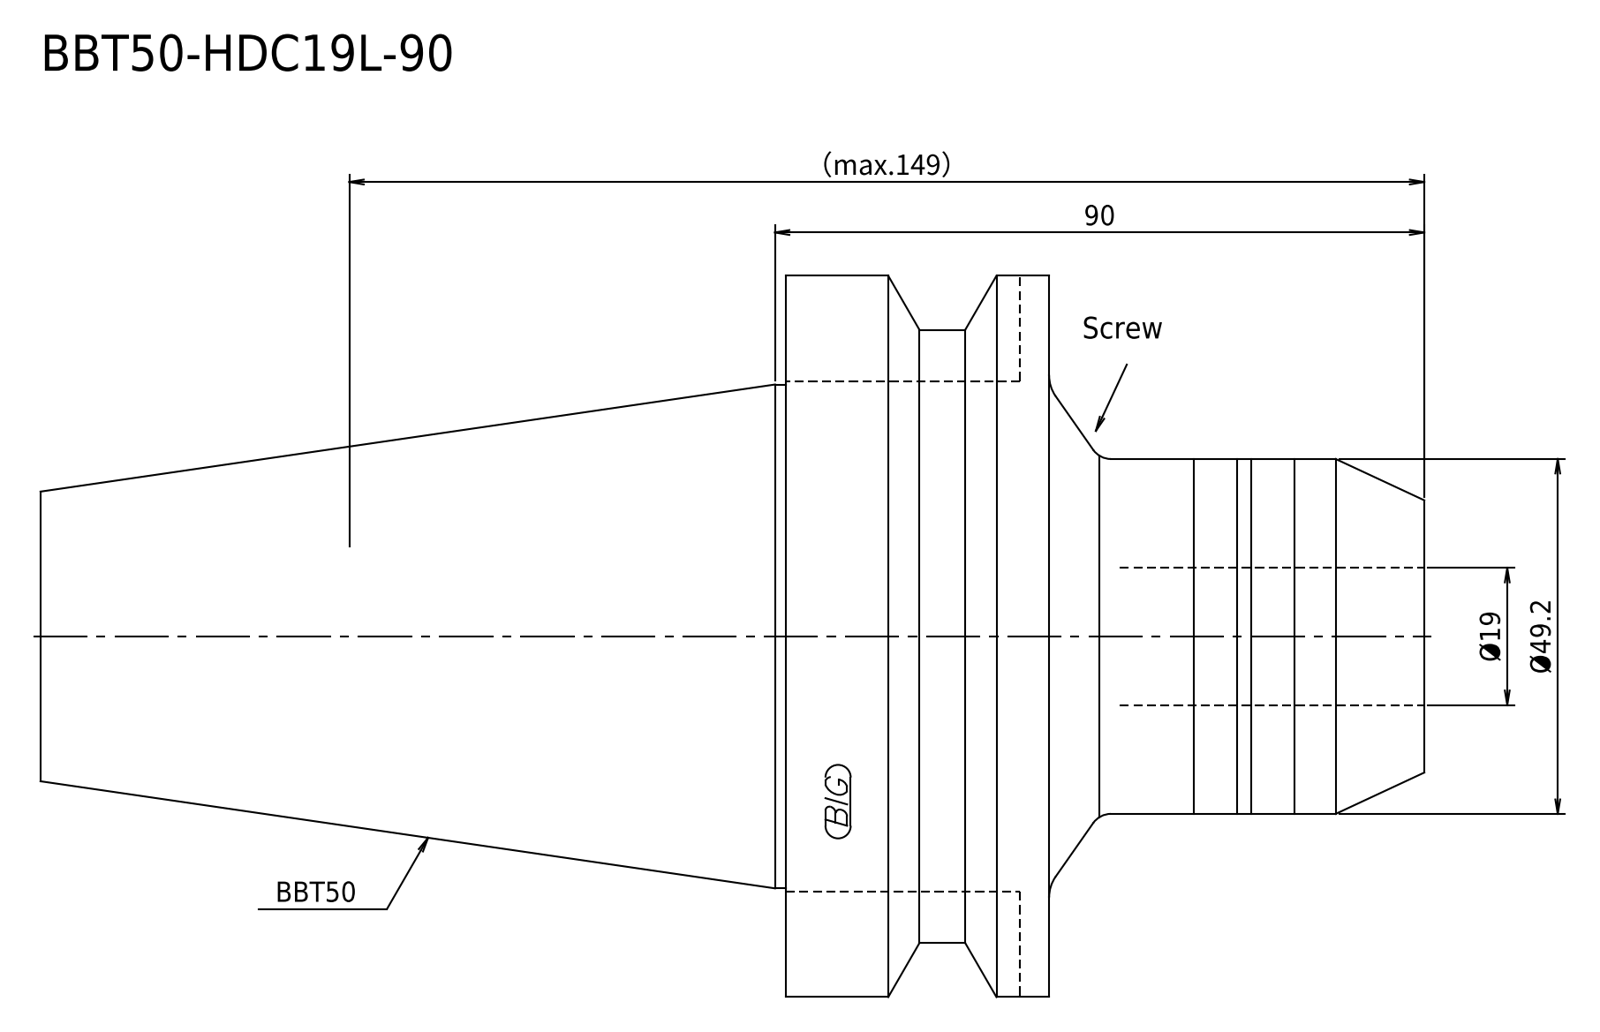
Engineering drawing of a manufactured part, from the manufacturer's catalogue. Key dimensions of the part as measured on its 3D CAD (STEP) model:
STEP written by: Kubotek KeyCreator V8.5.1 (14335) (CONFIG_CONTROL_DESIGN)
Units: millimetres
Bodies: 1 solid, 18 faces (5 planar, 5 cylindrical, 8 other)
Overall size (bounding box): 191.8 × 100 × 100
Volume: 616 532 mm³ · Surface area: 51 155 mm²
Round bosses / shafts (diameter × count): ⌀100 ×1, ⌀85 ×1, ⌀69.85 ×1, ⌀49.2 ×1
Main face-to-face distances: 36.5, 139.8, 103.3, 51.3, 87.8, 191.1, 0.7, 52, 88.5, 191.8
